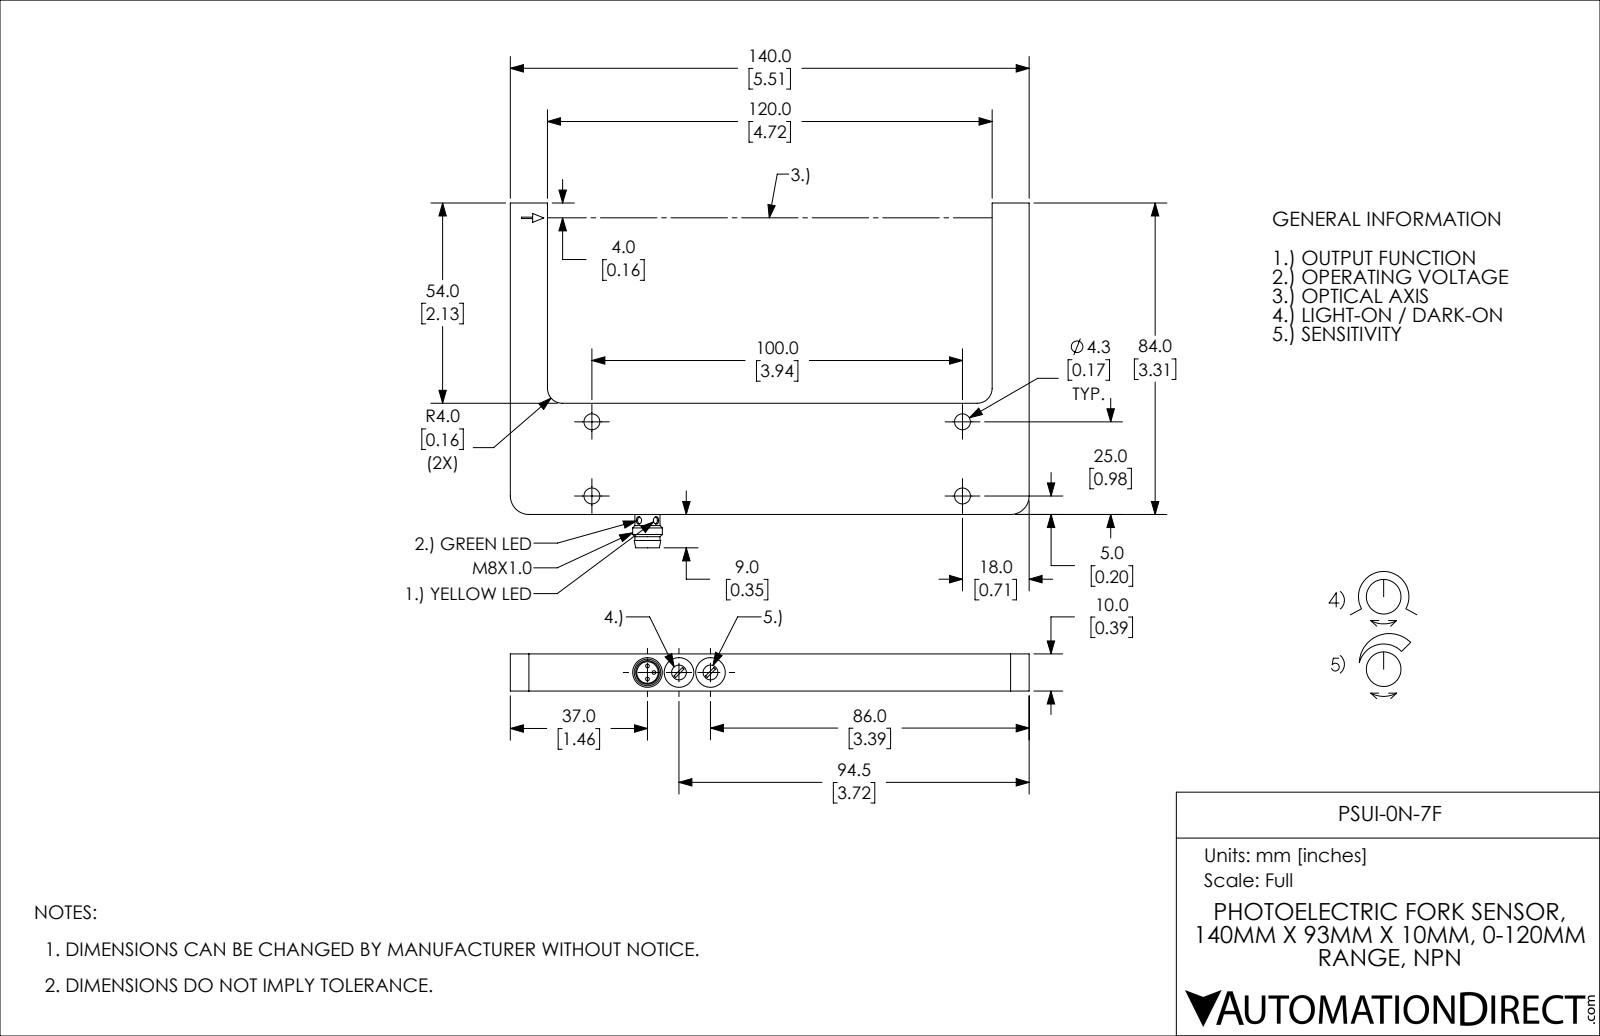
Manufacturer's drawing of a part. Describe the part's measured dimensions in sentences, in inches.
The part is named "PSUI-0N-7F". Its 3-D file was written by "SolidWorks 2017 (AUTOMOTIVE_DESIGN)". It is 1 solid with 68 faces: 35 planar, 27 cylindrical and 6 other. Overall it measures 5.512 by 3.661 by 0.394 inches. Its volume is 3.197 cubic inches and its surface area 26.09 square inches. Round holes: 4 of diameter 0.169, 2 of diameter 0.079, 2 of diameter 0.157, 2 of diameter 0.315, 1 of diameter 0.228. Round bosses or shafts: 3 of diameter 0.039, 1 of diameter 0.315, 1 of diameter 0.267. Partial cylindrical surfaces (rounded edges, fillets, slot ends): 2 of radius 0.063, 2 of radius 0.157, 2 of radius 0.197. The main face-to-face distances are 0.394, 1.181, 5.118, 5.512, 4.724, 2.126, 3.307, 3.303, 1.177, 0.157. The hole center spacings are 0.335, 0.787, 3.937, 4.015, 0.669.
